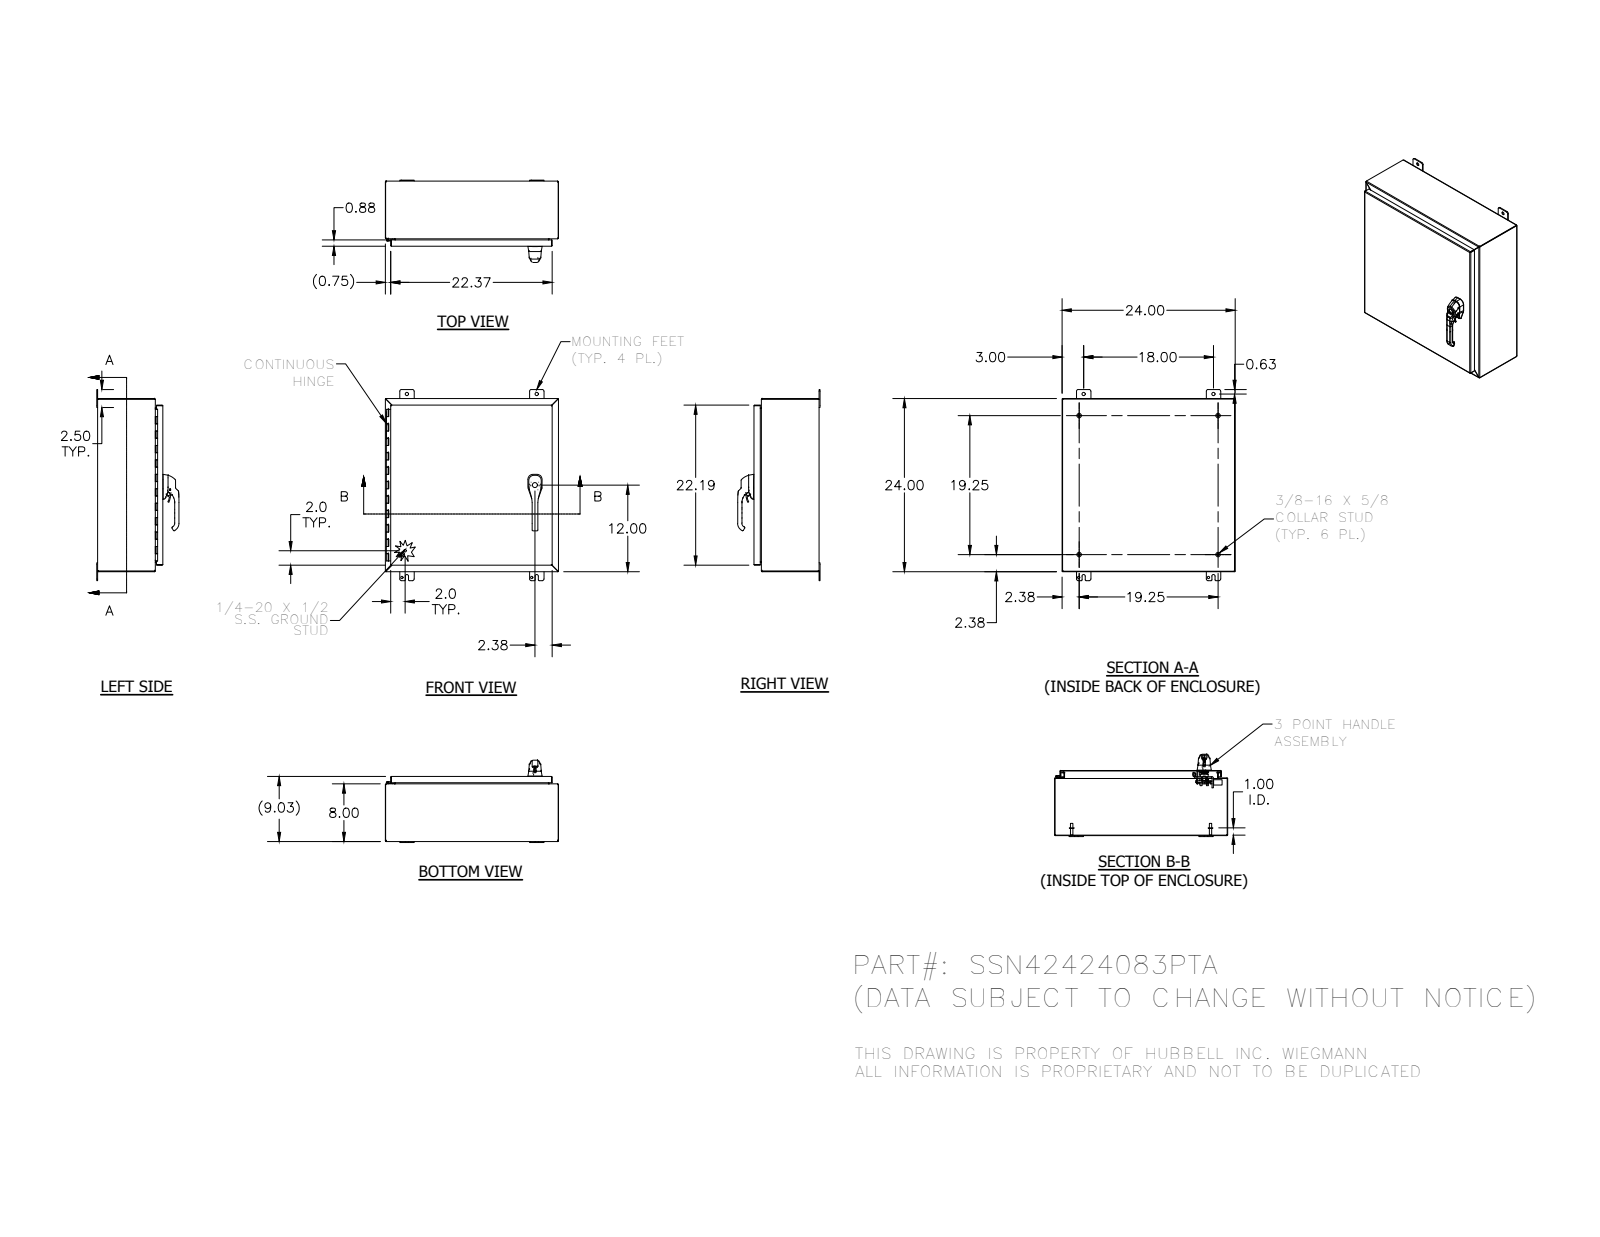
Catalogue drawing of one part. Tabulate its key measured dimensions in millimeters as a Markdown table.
| quantity | value |
| --- | --- |
| part name | SPACER; 328138P; 22x22; 328138T (+8 more) |
| STEP written by | SolidWorks 2014 (AUTOMOTIVE_DESIGN) |
| units | millimeters |
| bodies | 56 solids, 3071 faces (1014 planar, 1270 cylindrical, 787 other) |
| overall size | 673.1 × 609.6 × 289.8 |
| volume | 3 018 000 mm³ |
| surface area | 3 050 000 mm² |
| round holes (diameter × count) | 6.7 × 8, 4.7 × 4, 8 × 4, 11.1 × 4, 5.4 × 3, 7.1 × 3, 6.1 × 2, 6.4 × 2, 6.4 × 2, 8 × 2, 10.2 × 2, 10.2 × 2 |
| round bosses / shafts (diameter × count) | 15.9 × 4, 8.4 × 4, 6 × 3, 25.4 × 2, 14.3 × 2, 13.5 × 2, 13.5 × 2, 12.7 × 2 |
| partial cylindrical surfaces (radius × count) | 0.5 × 172, 0.3 × 113, 3.2 × 26, 0.8 × 24, 0.5 × 21, 2.7 × 20, 6.4 × 20, 0.6 × 16 |
| main face-to-face distances | 1.9, 227.6, 607.7, 225.7, 229.4, 605.8, 609.6, 201.3, 26.2, 203.2 |
| hole center spacings | 9.7, 12.5, 19.3, 40.5, 457.2, 609.6, 762, 22.5 |
